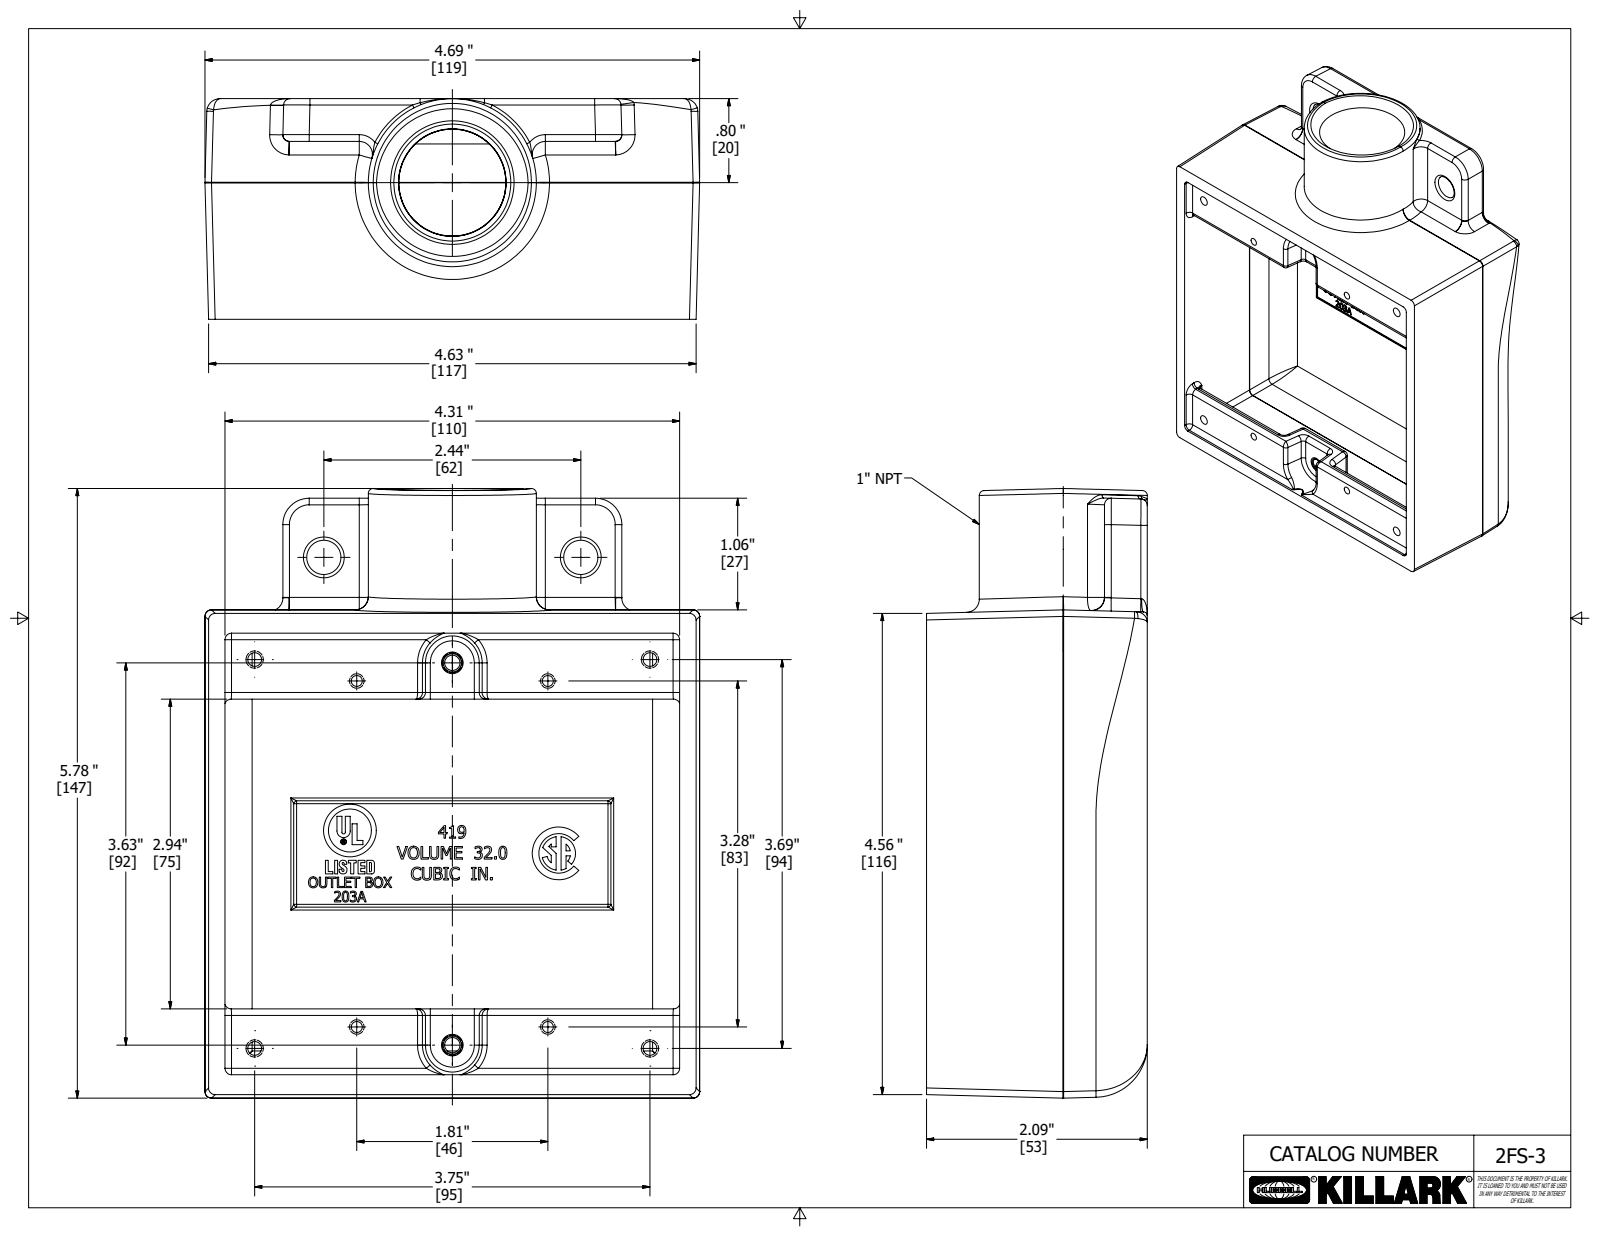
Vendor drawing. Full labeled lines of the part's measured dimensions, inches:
Part name (STEP PRODUCT): 23678-3
STEP written by: Autodesk Inventor 2020 (AUTOMOTIVE_DESIGN)
Units: inches
Bodies: 1 solid, 1193 faces (556 planar, 168 cylindrical, 469 other)
Overall size (bounding box): 5.781 × 4.693 × 2.094
Volume: 11.46 in³ · Surface area: 134.8 in²
Round holes (diameter × count): ⌀0.104 ×4, ⌀0.13 ×4, ⌀0.145 ×2, ⌀0.056 ×1, ⌀0.5 ×1
Round bosses / shafts (diameter × count): ⌀1.594 ×1, ⌀0.407 ×1, ⌀0.047 ×1
Partial cylindrical surfaces — rounded edges, fillets, slot ends (radius × count): R0.062 ×46, R0.031 ×16, R0.094 ×10, R0.125 ×9, R0.25 ×3, R0.281 ×3, R0.01 ×2, R0.011 ×2
Main face-to-face distances: 0.156, 1.843, 4.537, 4.474, 0.031, 1.812, 1.999, 4.693, 1.687, 4.317
Hole centre spacings: 0.922, 0.99, 1.875, 2.789, 3.57, 3.617, 4.109, 4.458
